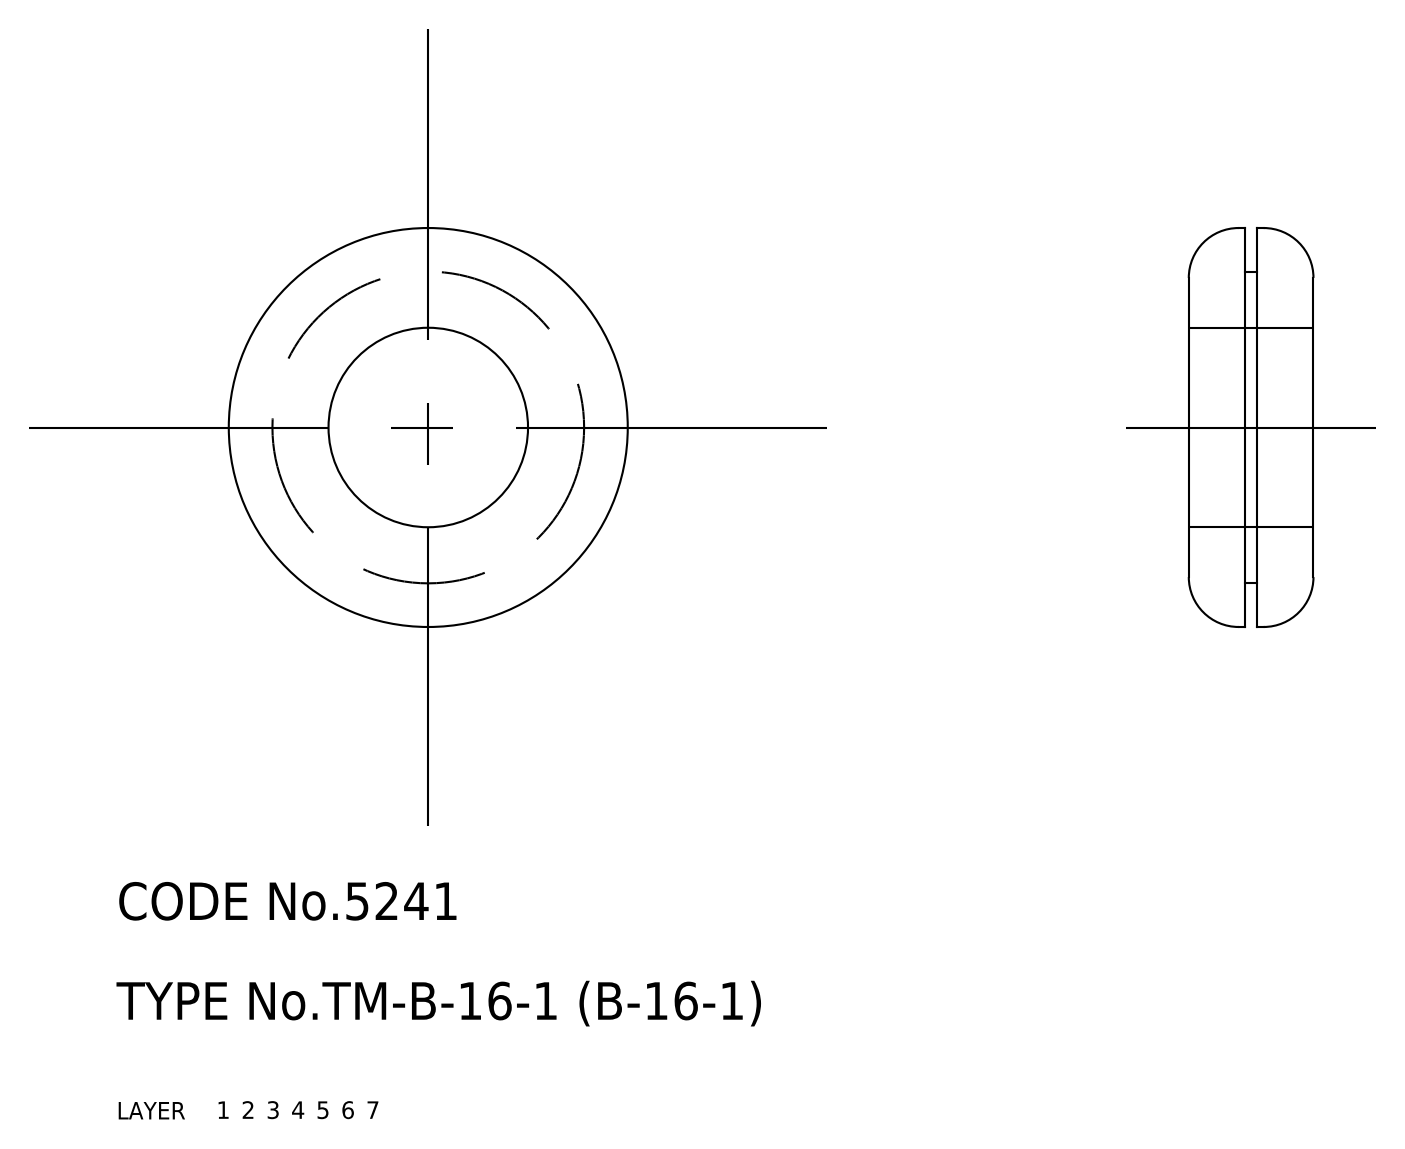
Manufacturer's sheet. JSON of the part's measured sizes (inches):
{"part_name": "grommet", "step_written_by": "CADfix (AUTOMOTIVE_DESIGN)", "units": "inches", "bodies": {"solids": 1, "faces": 16, "planar": 0, "cylindrical": 0, "other": 16}, "overall_size": [1.26, 1.26, 0.394], "volume_in3": 0.31, "surface_area_in2": 4.591}
